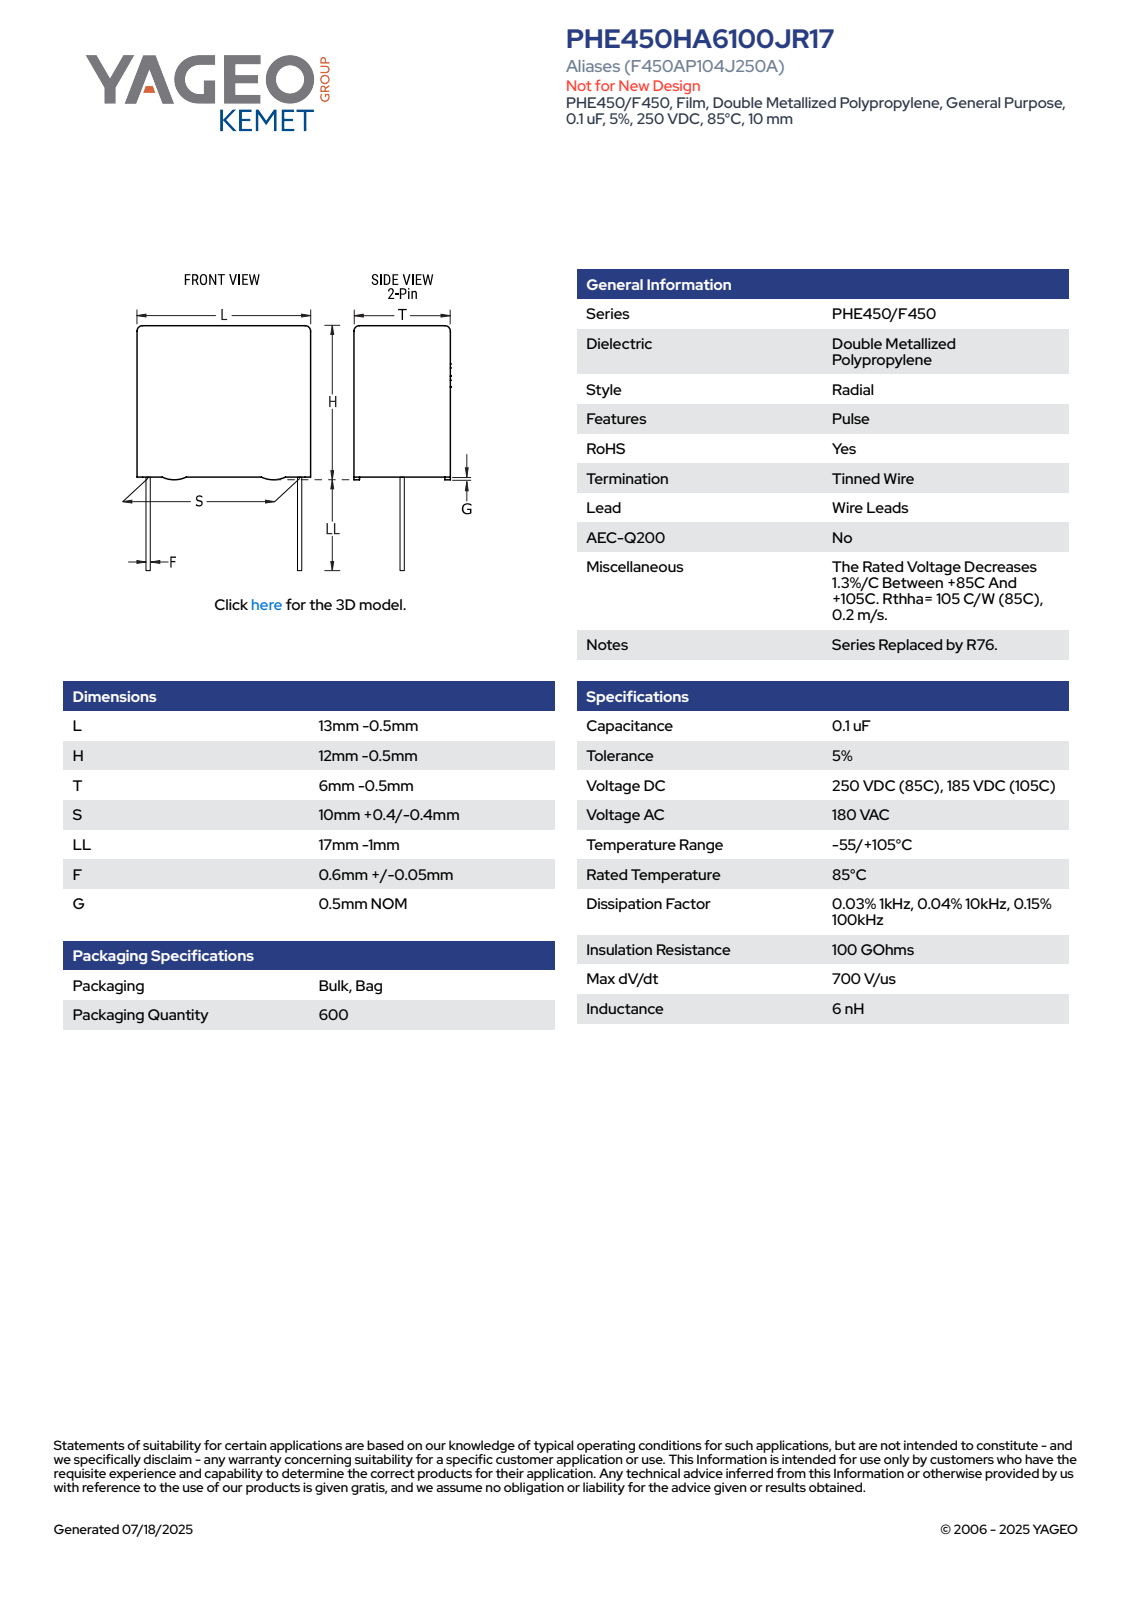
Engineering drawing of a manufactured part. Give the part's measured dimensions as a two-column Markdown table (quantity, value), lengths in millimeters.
| quantity | value |
| --- | --- |
| part name | CFR_RBG_13X12X6_L12.5H11.5T5.5S10LL16F0.65G0.5 |
| STEP written by | SolidWorks 2014 (AUTOMOTIVE_DESIGN) |
| units | millimeters |
| bodies | 4 solids, 89 faces (81 planar, 8 cylindrical, 0 other) |
| overall size | 27.5 × 12.5 × 5.5 |
| volume | 767 mm³ |
| surface area | 619 mm² |
| round bosses / shafts (diameter × count) | 0.65 × 2 |
| partial cylindrical surfaces (radius × count) | 0.5 × 4 |
| main face-to-face distances | 5.5, 12.5, 11, 0.31, 5.19, 0.5, 11.5, 4.88, 16, 16.5 |
